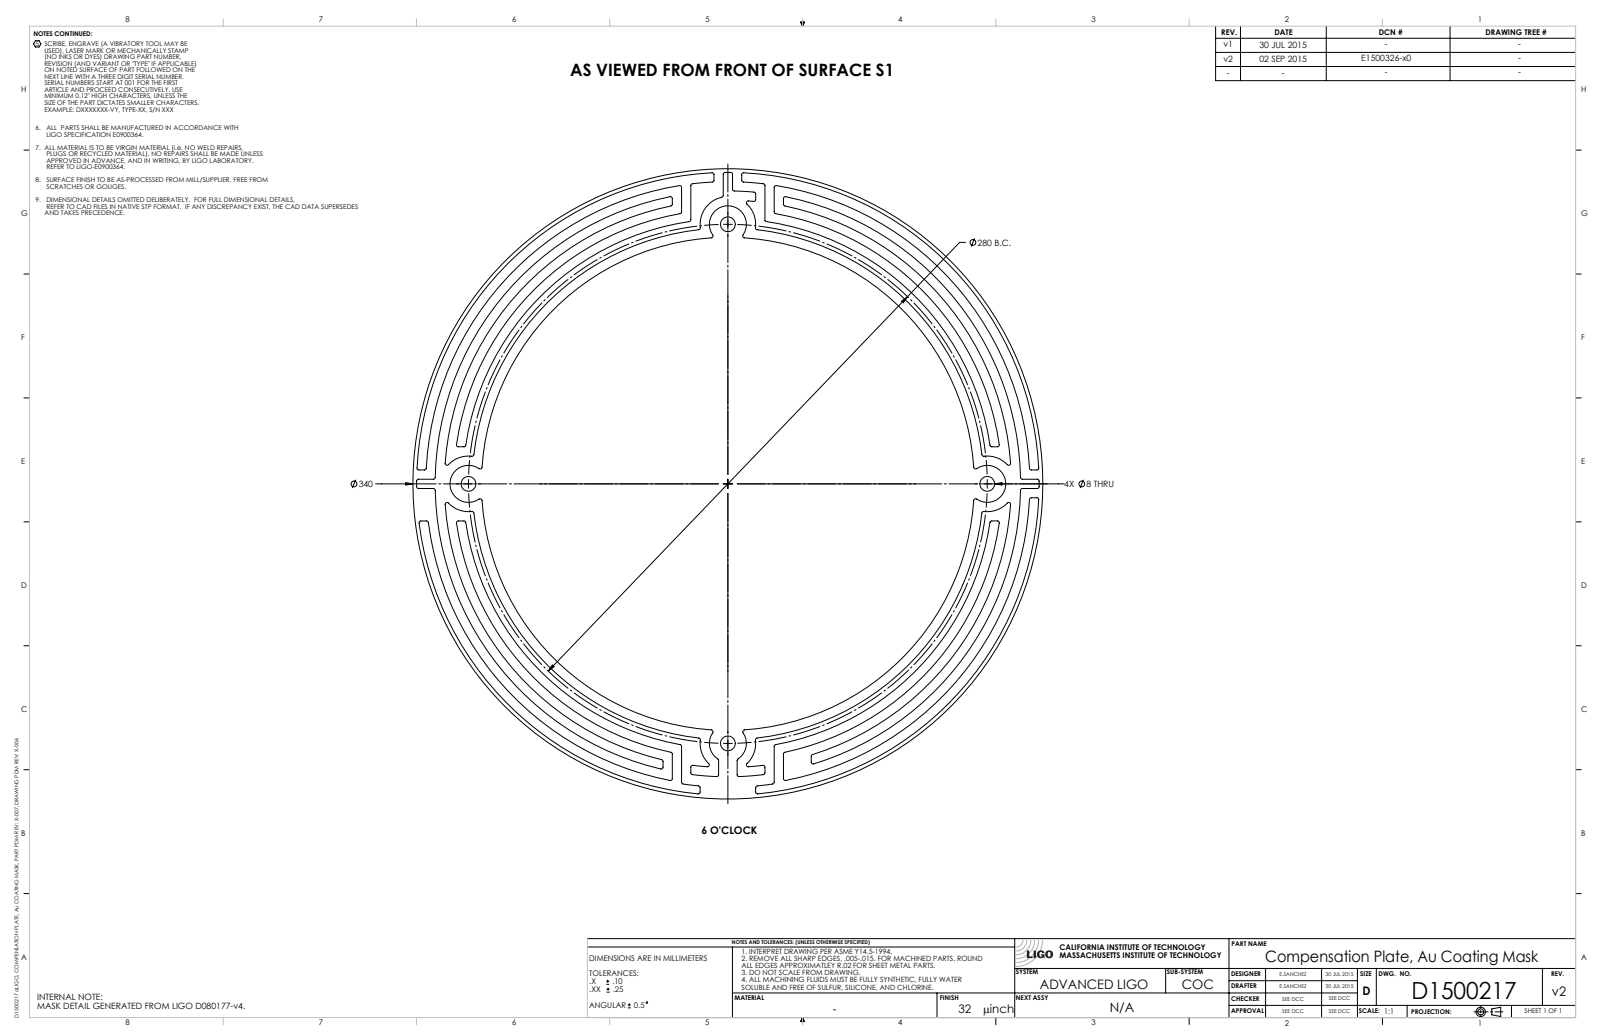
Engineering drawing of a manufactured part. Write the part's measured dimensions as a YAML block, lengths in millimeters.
part_name: "D1500217-v2"
step_written_by: "SolidWorks 2015 (AUTOMOTIVE_DESIGN)"
units: millimeters
bodies: {solids: 1, faces: 221, planar: 37, cylindrical: 184, other: 0}
overall_size: [340, 340, 1.27]
volume: 92161
surface_area: 155731
round_holes:
  - {diameter: 8, count: 4}
  - {diameter: 276, count: 1}
  - {diameter: 316, count: 1}
  - {diameter: 336, count: 1}
round_bosses_or_shafts:
  - {diameter: 340, count: 1}
  - {diameter: 326, count: 1}
  - {diameter: 306, count: 1}
  - {diameter: 286, count: 1}
  - {diameter: 266, count: 1}
partial_cylinders:
  - {radius: 1, count: 93}
  - {radius: 10, count: 4}
  - {radius: 15, count: 3}
  - {radius: 15, count: 1}
  - {radius: 15, count: 1}
  - {radius: 148, count: 1}
  - {radius: 163.69, count: 1}
face_to_face_distances: [1.27, 5, 50, 10, 22.5, 27.5, 45, 17.5, 40, 55]
hole_center_spacings: [140, 197.99, 280]
